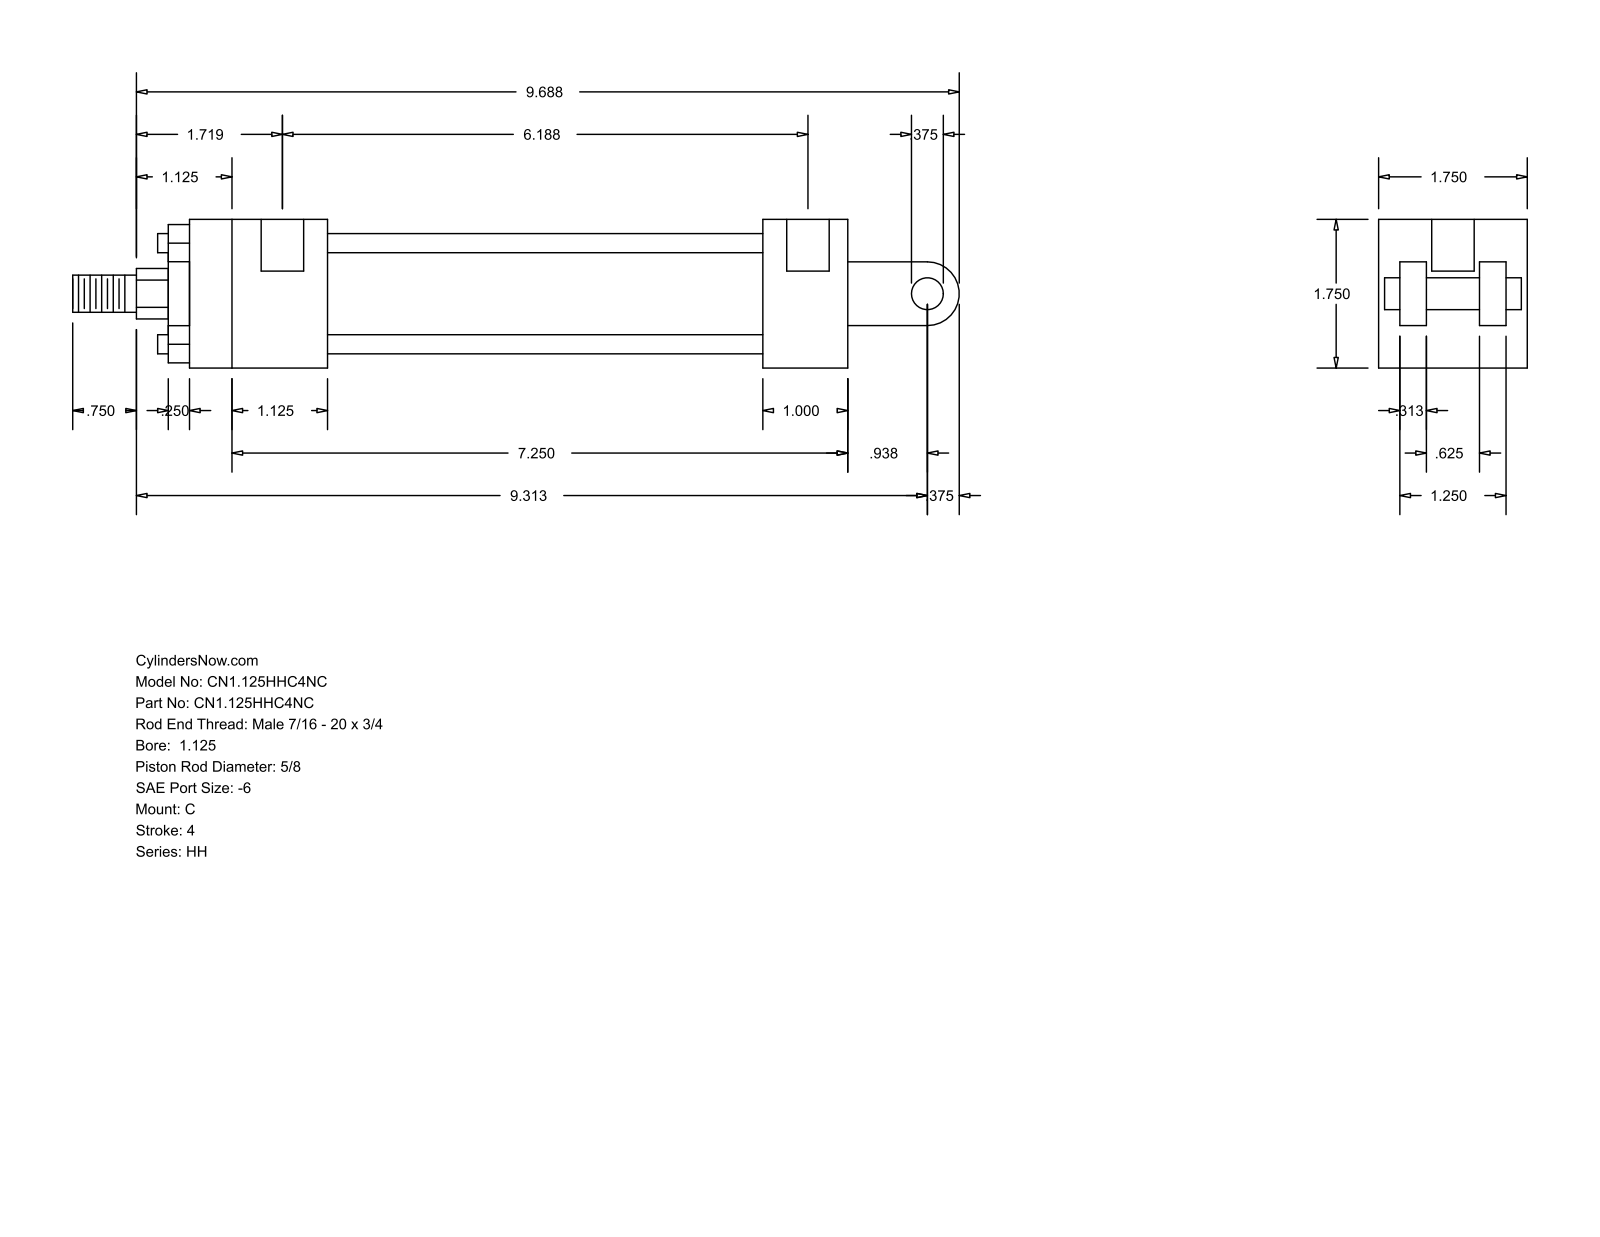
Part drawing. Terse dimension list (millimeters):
name: HH_C__0112_0.625
written by: GSSL Pune (CONFIG_CONTROL_DESIGN)
unit: mm
bodies: 0 solids, 99 faces (70 planar, 29 cylindrical, 0 other)
size: 265.11 × 44.45 × 44.45
holes: 4× ⌀5.56, 2× ⌀12.7
bosses: 4× ⌀5.71, 1× ⌀34.92, 1× ⌀28.57, 1× ⌀15.88, 1× ⌀11.11, 1× ⌀9.53
rounds: 1× R7.54, 1× R9.53
face distances: 44.46, 6.35, 31.76, 14.29, 25.4, 30.17, 38.11, 7.94, 23.82, 41.27
hole spacings: 153.99, 3.17, 157.16
